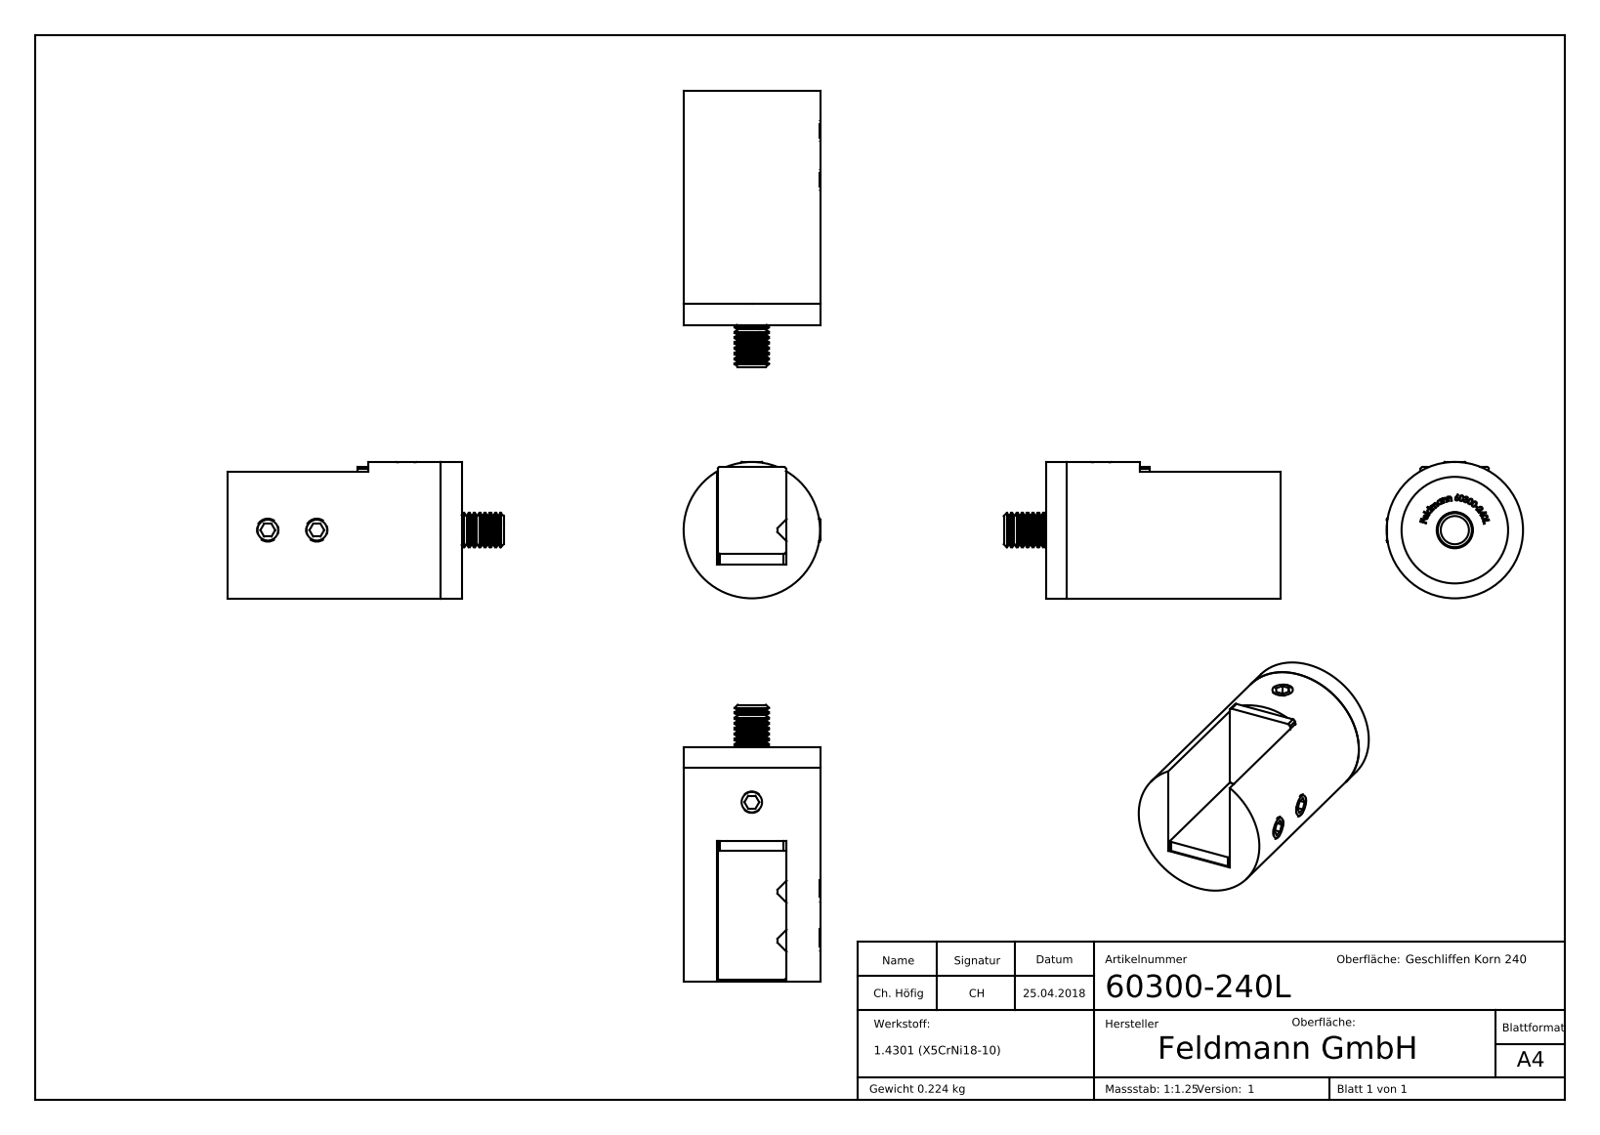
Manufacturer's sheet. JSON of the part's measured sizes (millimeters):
{"part_name": "6030X-240X Teil1_6030X-240L Teil1; socket countersunk head screw_din_DIN 7991 - M8 x 25 --- 25S; 6030X-240X Teil2_6030X-240X Teil2; socket set screw cone point_din (+8 more)", "step_written_by": "SolidWorks 2018 (CONFIG_CONTROL_DESIGN)", "units": "millimeters", "bodies": {"solids": 8, "faces": 427, "planar": 180, "cylindrical": 52, "other": 195}, "overall_size": [70, 64.85, 32], "volume_mm3": 31669, "surface_area_mm2": 16400, "round_holes": [[5, 3], [8.5, 1], [25, 1]], "round_bosses_or_shafts": [[6, 3], [32, 1], [20, 1], [15.57, 1], [8, 1]], "partial_cylinders_radius": [[0.5, 8]], "face_to_face_distances": [2.45, 16.3, 17, 3.3, 20.3, 53.3, 50, 33, 22.75, 19.45], "hole_center_spacings": [11.5]}
